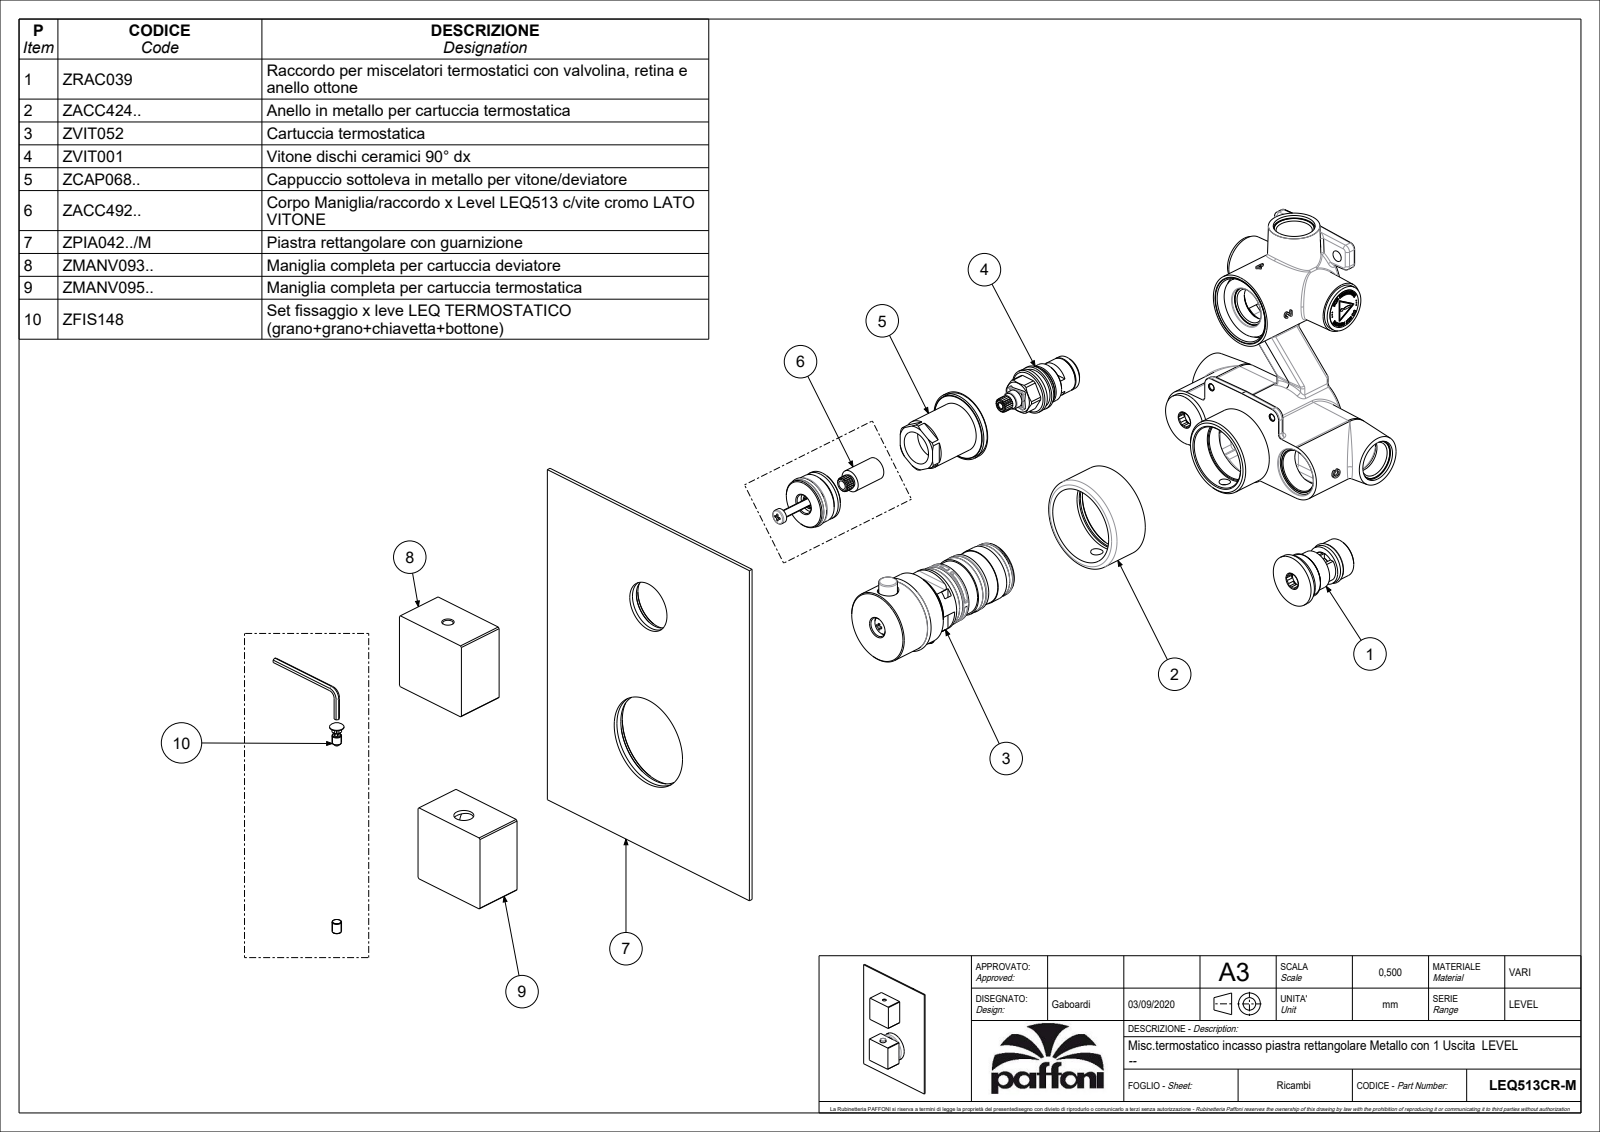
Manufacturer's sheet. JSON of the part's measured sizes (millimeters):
{"part_name": "LEQ513CR-M", "step_written_by": "CREO PARAMETRIC BY PTC INC, 2020044 (CONFIG_CONTROL_DESIGN)", "units": "millimeters", "bodies": {"solids": 1, "faces": 409, "planar": 190, "cylindrical": 185, "other": 34}, "overall_size": [200, 150, 40.01], "volume_mm3": 188351, "surface_area_mm2": 83586, "round_holes": [[34.4, 1], [35.8, 1], [41.5, 1]], "round_bosses_or_shafts": [[7.6, 2], [49.9, 1], [41, 1], [39, 1], [26.8, 1], [9.9, 1]], "partial_cylinders_radius": [[0.15, 60], [0.5, 6], [0.2, 5], [0.1, 2], [0.8, 2], [31, 2], [3, 1], [3.25, 1]], "face_to_face_distances": [2, 43, 82, 46, 38.81, 36.81, 40.01, 38.01, 1.2, 10.81]}
